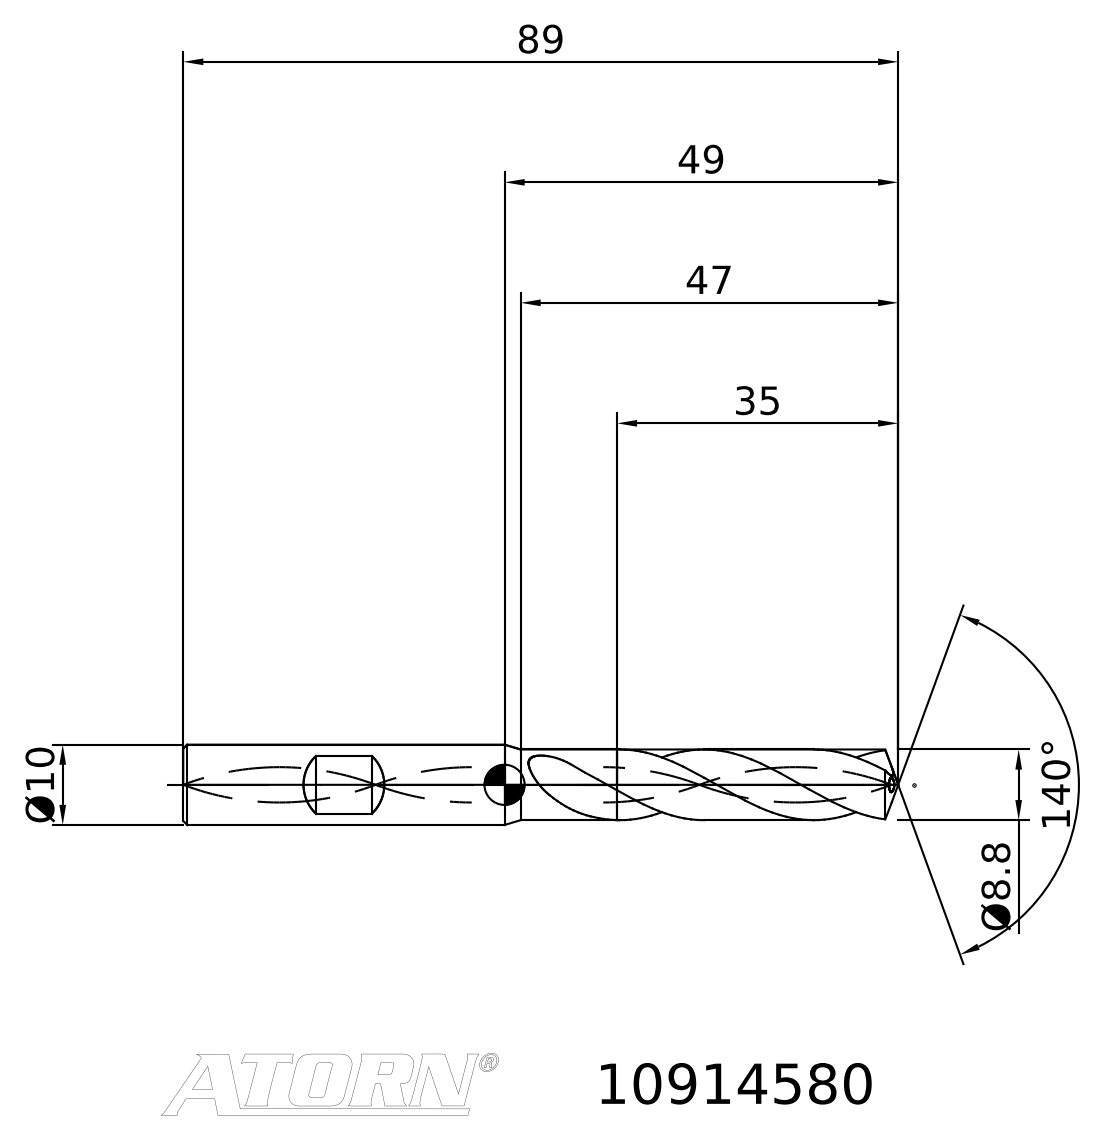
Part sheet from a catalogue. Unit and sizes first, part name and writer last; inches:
Units: inches
Overall size (bounding box): 3.504 × 0.877 × 0.546
Main face-to-face distances: 2.126, 1.331, 3.457
Volume: 0.313 in³ · Surface area: 4.473 in²
Bodies: 2 solids, 33 faces (8 planar, 0 cylindrical, 25 other)
STEP written by: TDM (AUTOMOTIVE_DESIGN)
